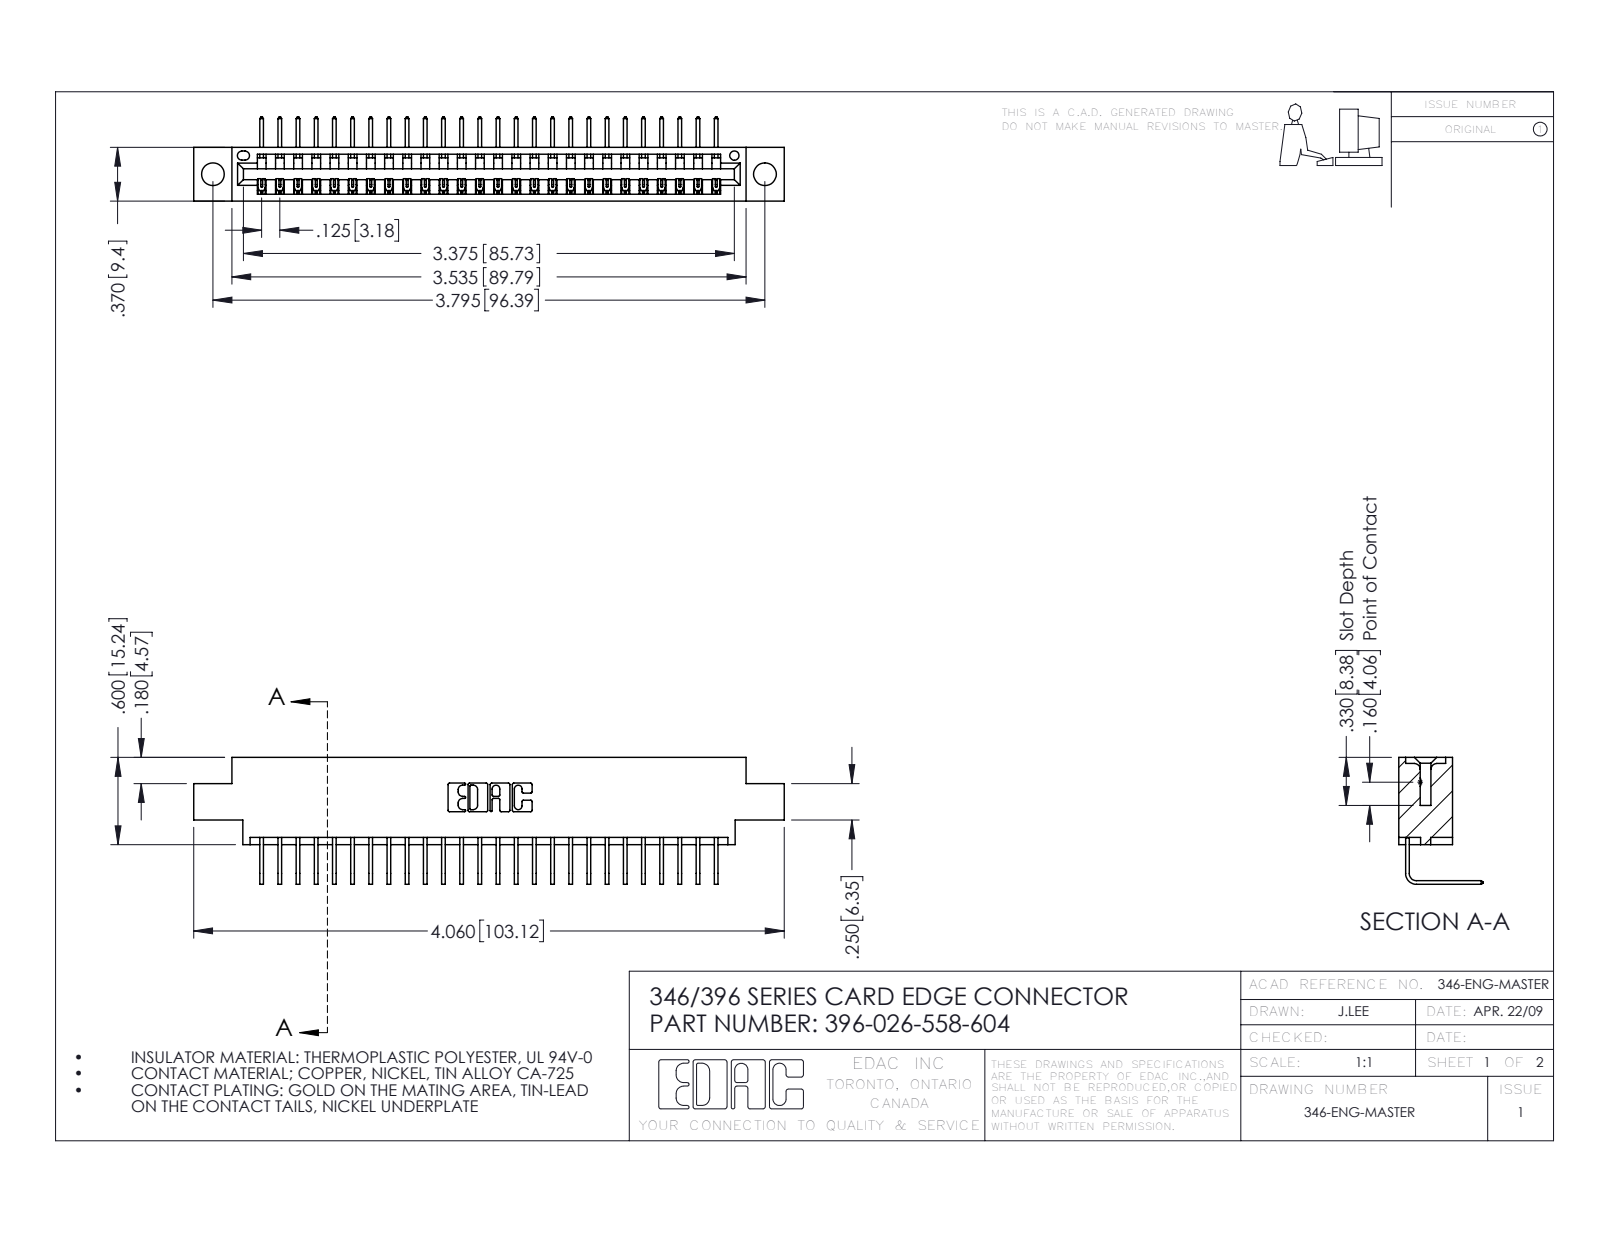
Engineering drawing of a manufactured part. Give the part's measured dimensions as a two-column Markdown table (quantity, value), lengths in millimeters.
| quantity | value |
| --- | --- |
| part name | 345-292-001_558 Tail - 2; 396-026-558-604; 346 Part_0.170 Offset - 0.156 Dia-TH |
| STEP written by | SolidWorks 2016 (CONFIG_CONTROL_DESIGN) |
| units | millimeters |
| bodies | 27 solids, 1686 faces (1172 planar, 514 cylindrical, 0 other) |
| overall size | 103.1 × 22.2 × 14.7 |
| volume | 9 600 mm³ |
| surface area | 12 320 mm² |
| round holes (diameter × count) | 4 × 2, 1.6 × 1 |
| partial cylindrical surfaces (radius × count) | 0.2 × 52, 0.3 × 22, 0.2 × 6, 0.8 × 6, 0.7 × 3, 0.8 × 2, 1 × 2, 0.4 × 1 |
| main face-to-face distances | 8.2, 1.2, 9.4, 6.4, 7.6, 0.6, 1.8, 3.8, 5.6, 2.5 |
| hole center spacings | 6.2, 91.1, 96.4 |
